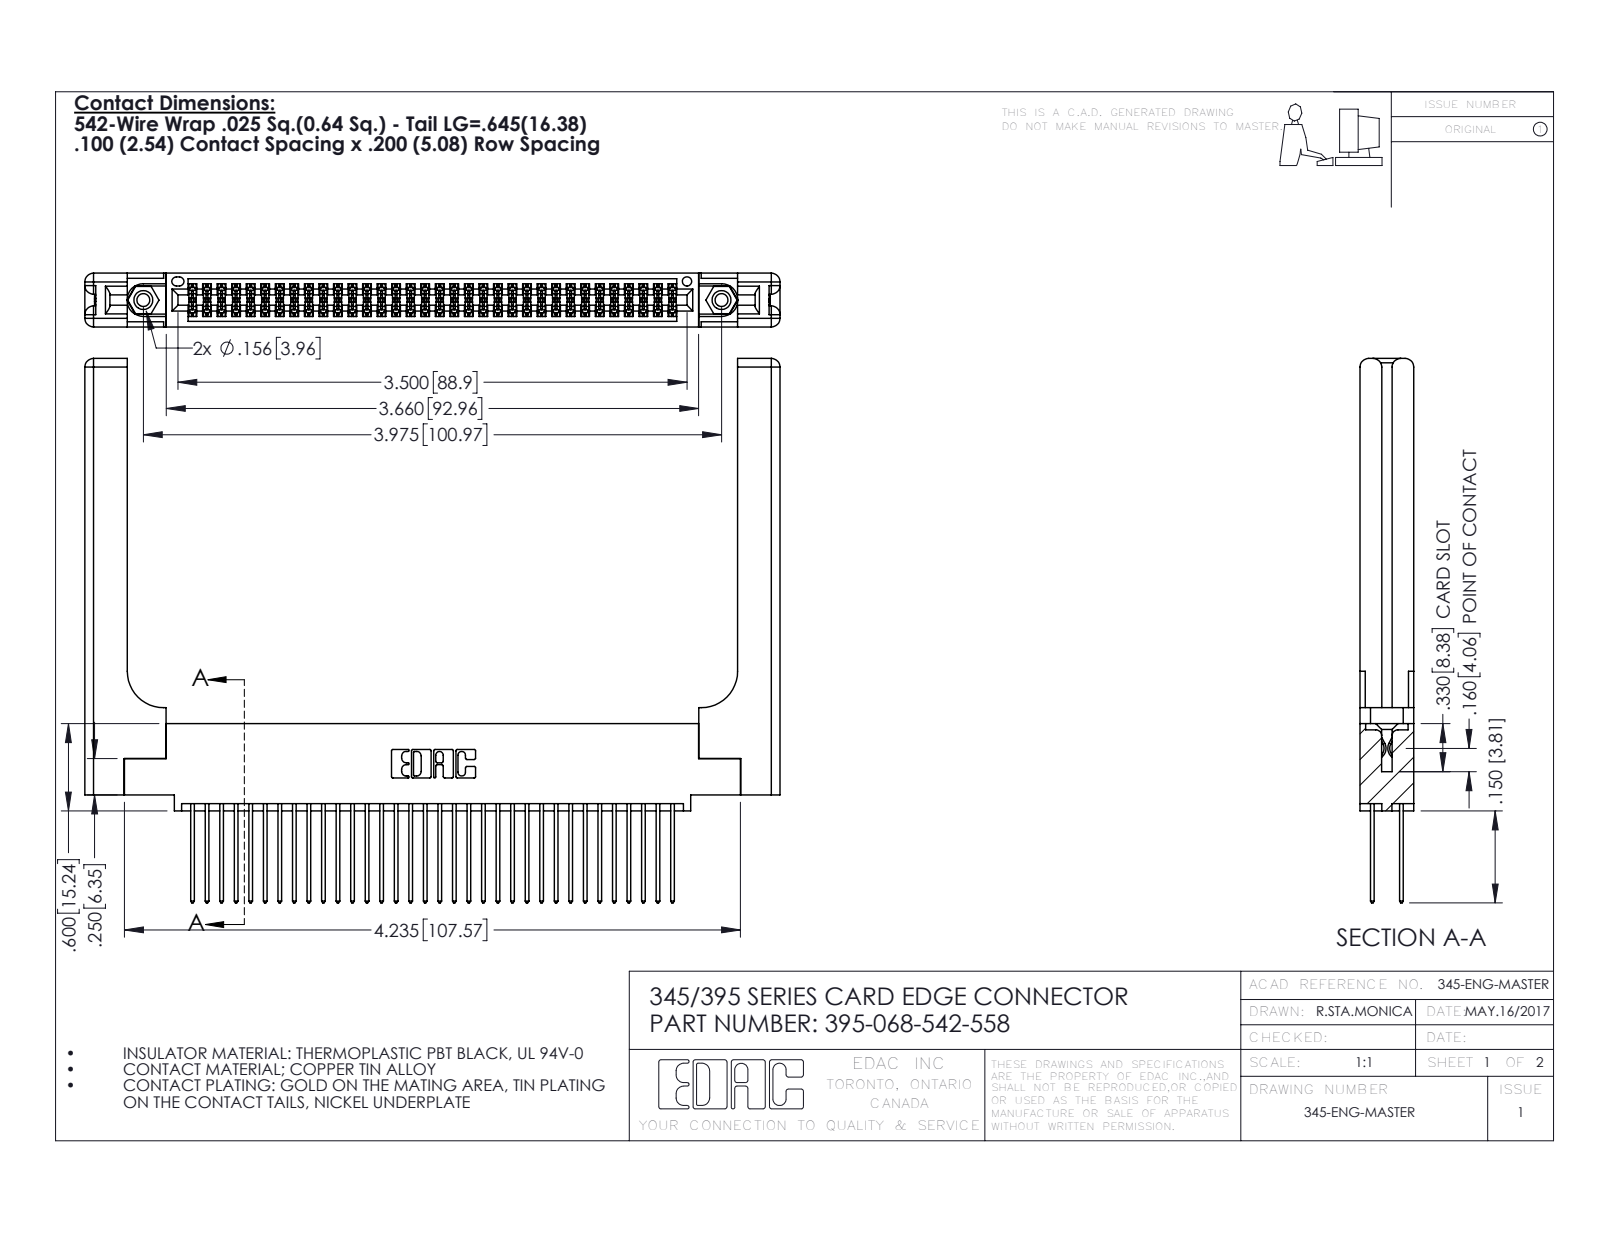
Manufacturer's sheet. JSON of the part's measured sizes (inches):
{"part_name": "345-292-001_345-293-142; 345-220-058_345-220-058; 345-250-001_345-250-001-102; 345 Part_0.110 Offset - 0.156 Dia-TH (+1 more)", "step_written_by": "SolidWorks 2016 (CONFIG_CONTROL_DESIGN)", "units": "inches", "bodies": {"solids": 73, "faces": 3786, "planar": 2476, "cylindrical": 1250, "other": 60}, "overall_size": [4.779, 3.742, 0.37], "volume_in3": 1.247, "surface_area_in2": 37.45, "round_holes": [[0.089, 2], [0.125, 2], [0.156, 2], [0.064, 1]], "round_bosses_or_shafts": [[0.155, 2]], "partial_cylinders_radius": [[0.006, 102], [0.01, 68], [0.01, 22], [0.06, 16], [0.007, 6], [0.031, 6], [0.026, 3], [0.014, 2]], "face_to_face_distances": [0.072, 0.298, 0.37, 0.2, 0.098, 0.272, 0.025, 0.225, 0.148, 0.15], "hole_center_spacings": [0.27, 3.74, 3.975]}
